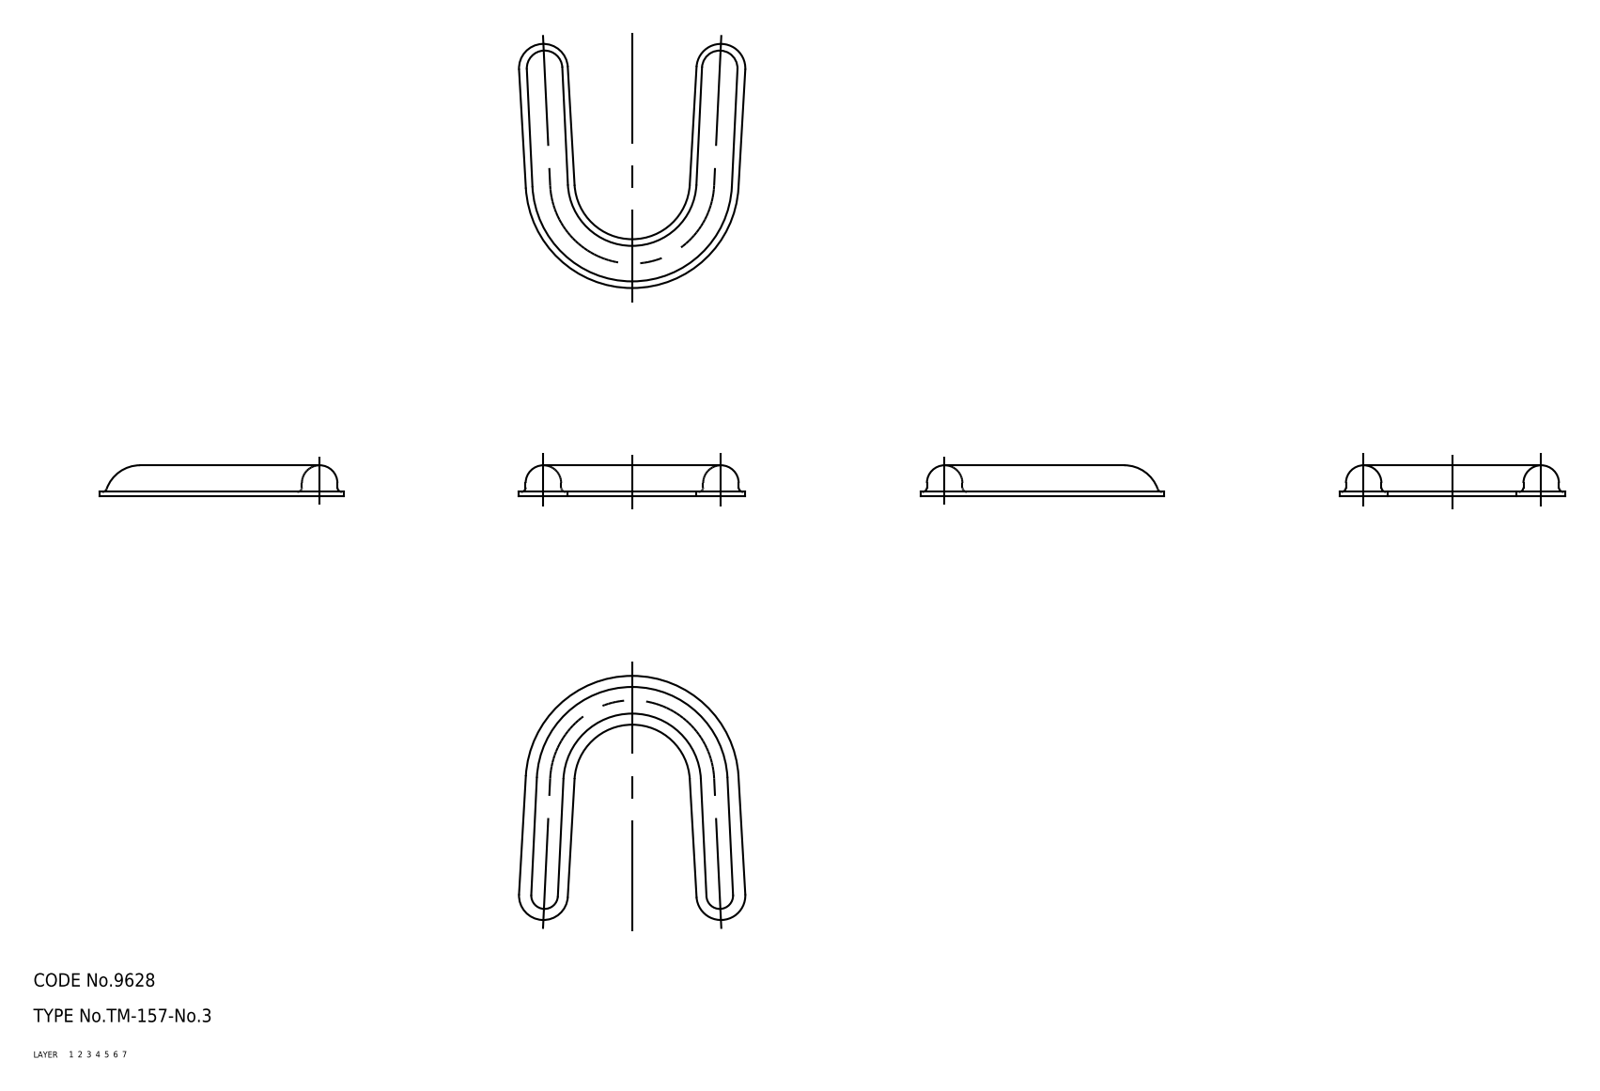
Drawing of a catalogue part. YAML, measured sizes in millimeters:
part_name: "holder"
step_written_by: "CADfix (AUTOMOTIVE_DESIGN)"
units: millimeters
bodies: {solids: 1, faces: 87, planar: 0, cylindrical: 0, other: 87}
overall_size: [55.01, 50.48, 7]
volume: 2361
surface_area: 4772
